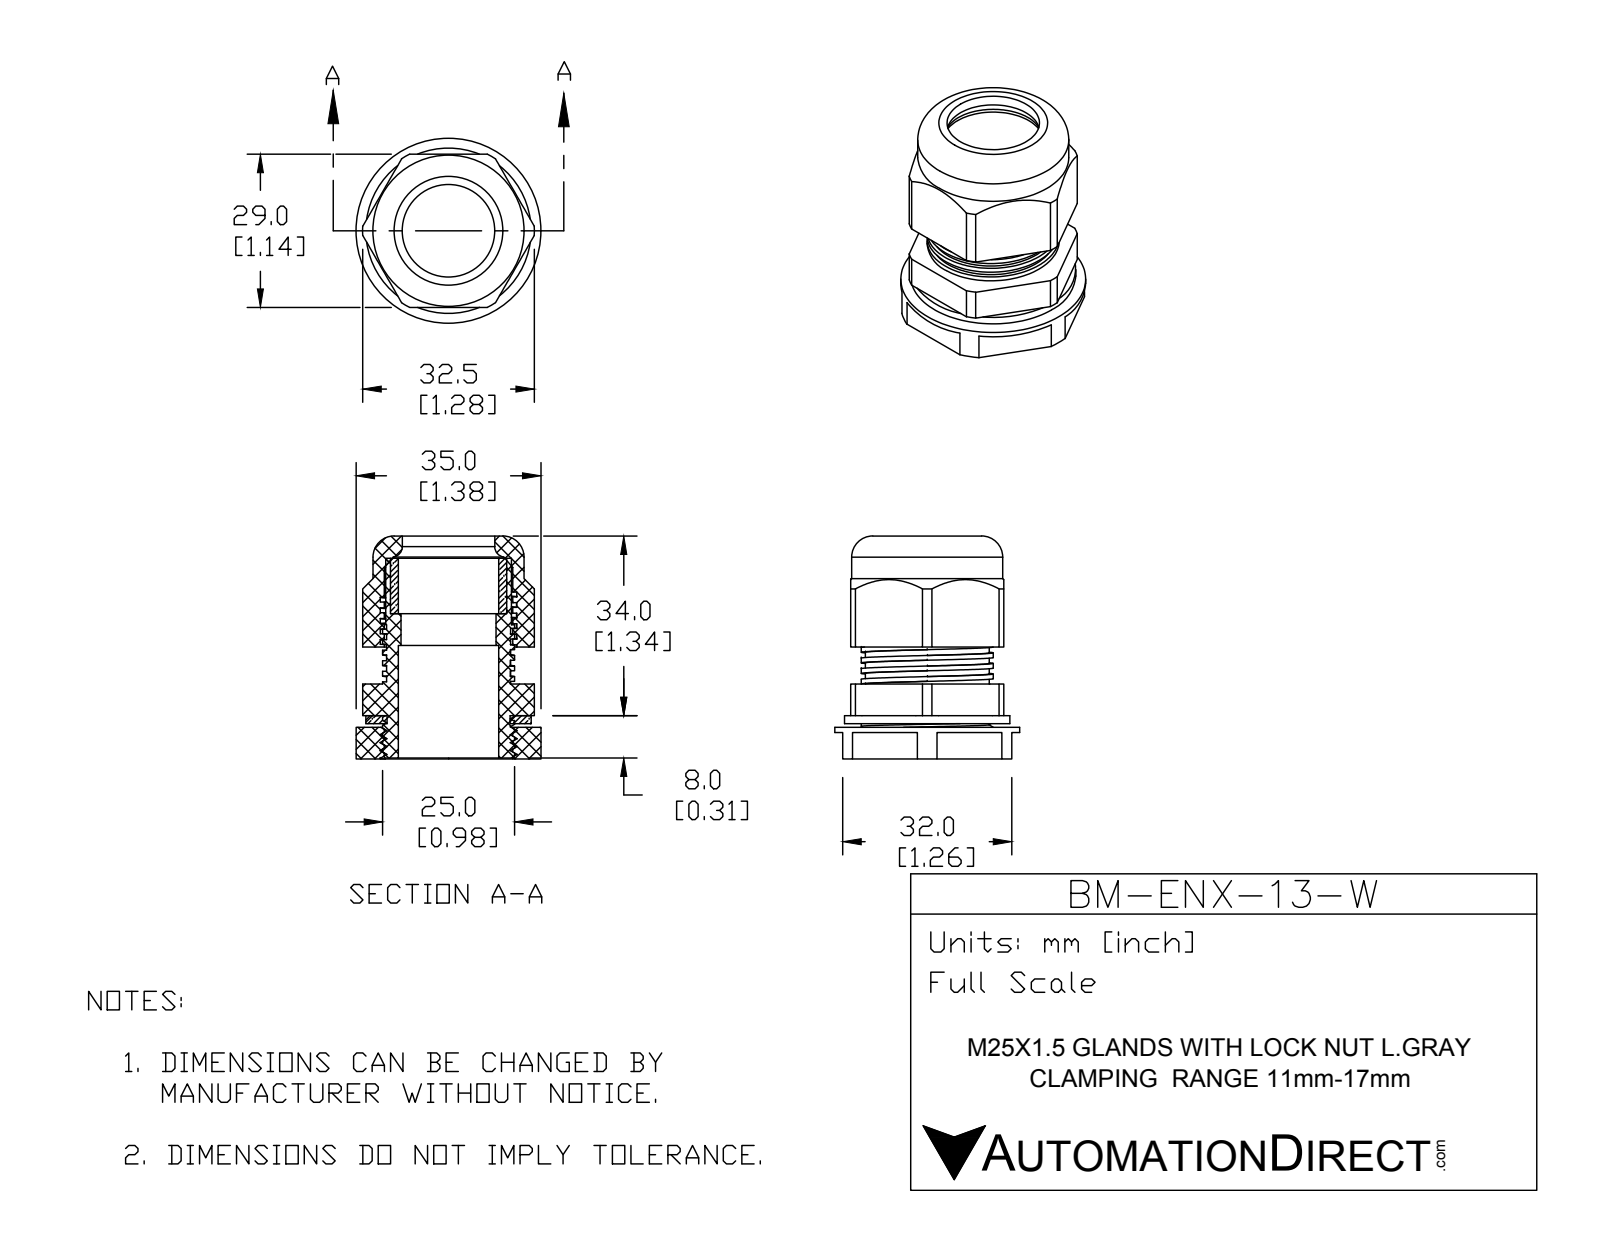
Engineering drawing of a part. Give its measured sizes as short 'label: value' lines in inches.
name: BM-ENX-13-W
written by: SolidWorks 2015 (CONFIG_CONTROL_DESIGN)
unit: in
bodies: 5 solids, 245 faces (141 planar, 82 cylindrical, 22 other)
size: 1.661 × 1.378 × 1.378
volume: 0.995 in³; area: 26.56 in²
holes: 1× ⌀0.689, 1× ⌀0.709, 1× ⌀0.748, 1× ⌀0.866, 1× ⌀0.917, 1× ⌀0.958
bosses: 1× ⌀1.378, 1× ⌀1.232, 1× ⌀1.126, 1× ⌀0.984, 1× ⌀0.937
rounds: 1× R0.64
face distances: 1.142, 0.059, 0.236, 0.322, 0.086, 1.201, 0.263, 0.027, 0.559, 0.295
